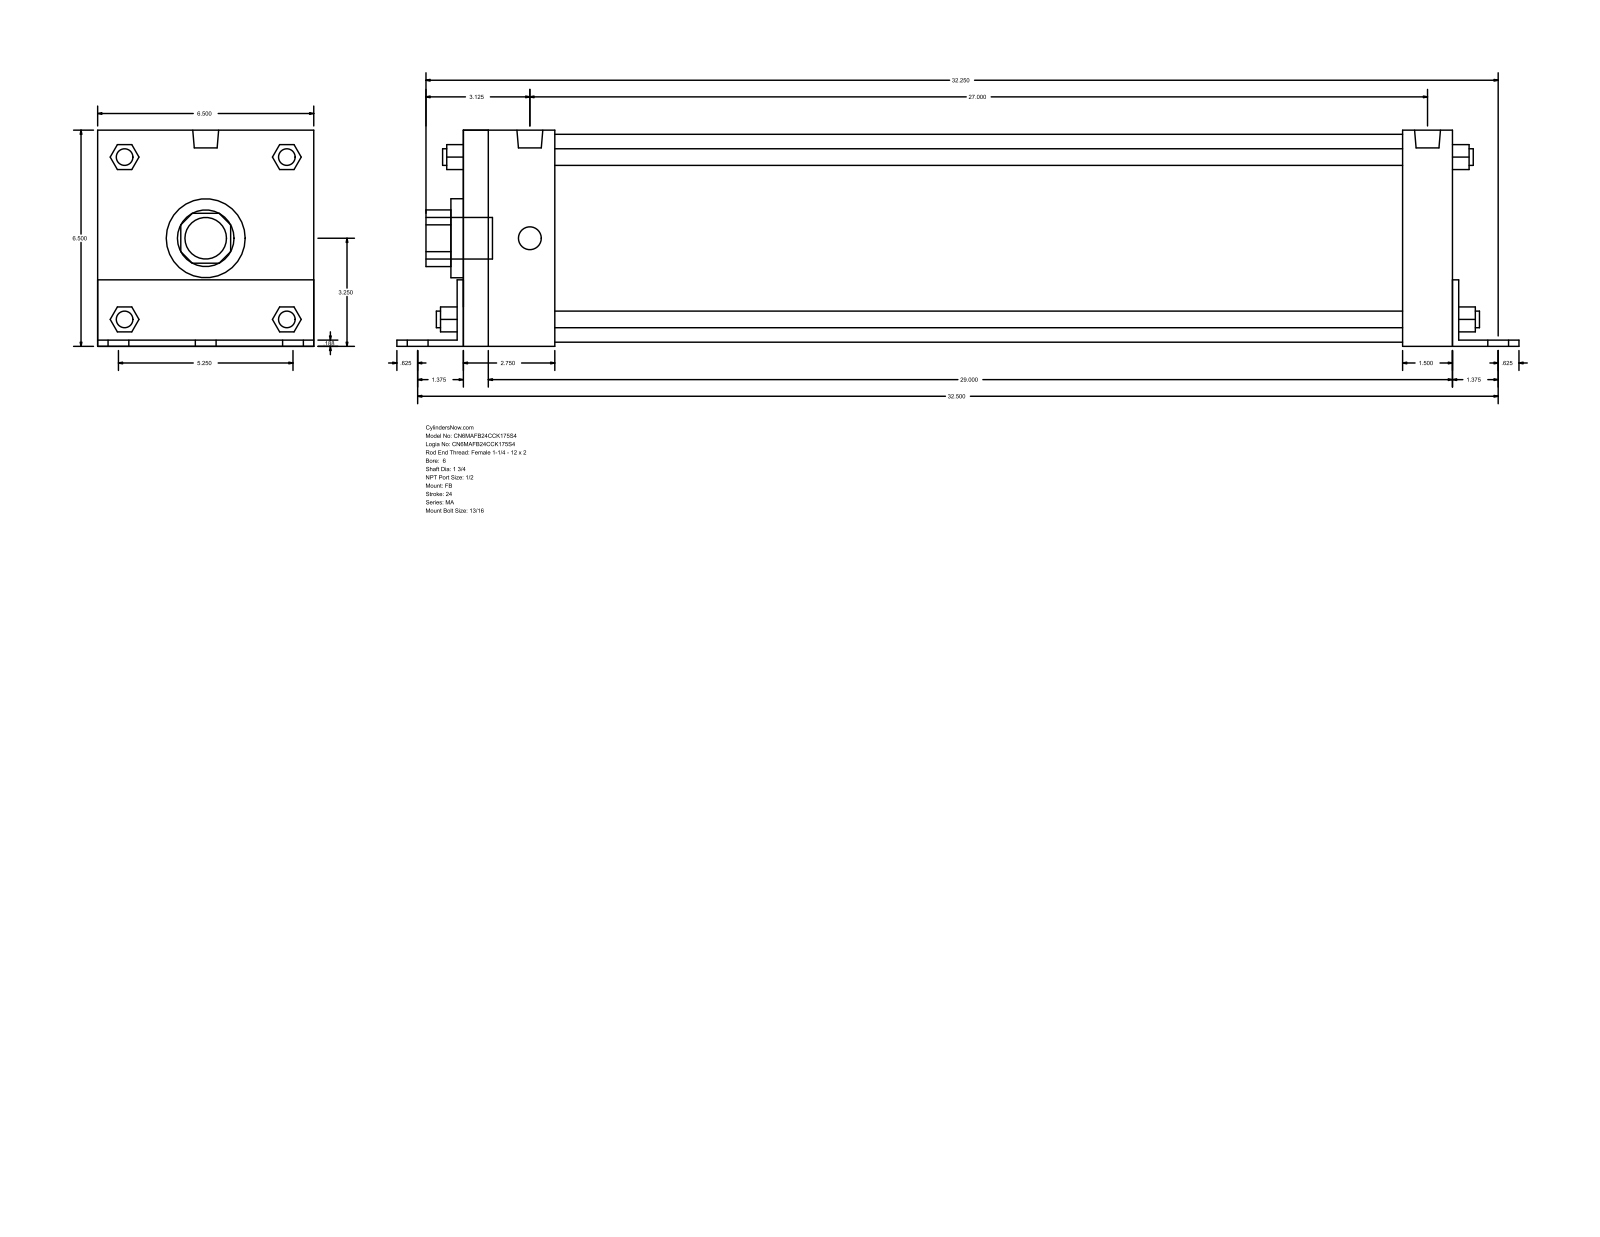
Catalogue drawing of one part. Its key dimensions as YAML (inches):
part_name: "MA_FB__0600_1.75"
step_written_by: "GSSL Pune (CONFIG_CONTROL_DESIGN)"
units: inches
bodies: {solids: 0, faces: 140, planar: 105, cylindrical: 35, other: 0}
overall_size: [33.75, 6.502, 6.5]
round_holes:
  - {diameter: 1.75, count: 1}
  - {diameter: 2.375, count: 1}
  - {diameter: 6.25, count: 1}
round_bosses_or_shafts:
  - {diameter: 0.813, count: 6}
  - {diameter: 0.687, count: 4}
  - {diameter: 0.5, count: 4}
  - {diameter: 0.778, count: 2}
  - {diameter: 1.25, count: 1}
partial_cylinders:
  - {radius: 0.852, count: 1}
  - {radius: 1.262, count: 1}
face_to_face_distances: [6.5, 0.187, 29.75, 6.502, 29.938, 0.185, 6.315, 30.125, 1.5, 2.937]
